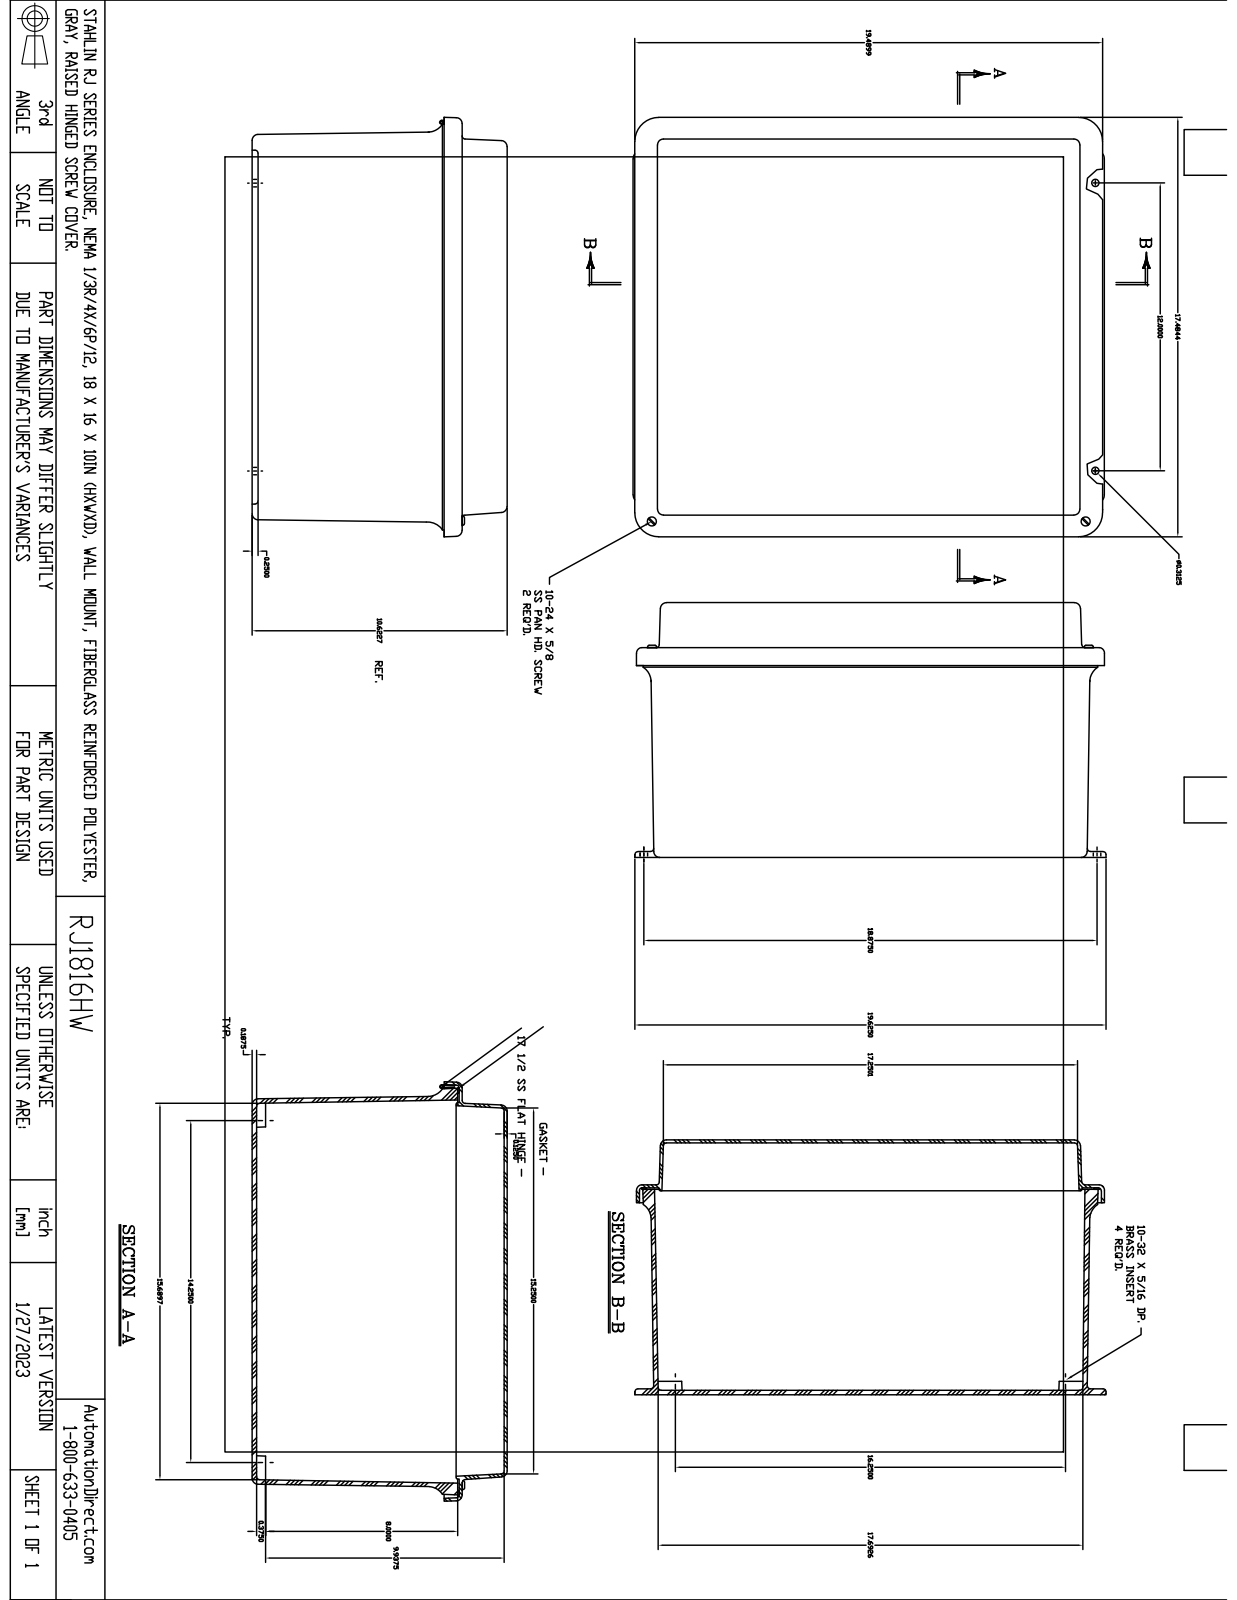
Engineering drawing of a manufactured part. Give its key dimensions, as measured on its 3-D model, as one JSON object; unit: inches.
{"part_name": "MR1816HW", "step_written_by": "SolidWorks 2018 (AUTOMOTIVE_DESIGN)", "units": "inches", "bodies": {"solids": 26, "faces": 1012, "planar": 390, "cylindrical": 389, "other": 233}, "overall_size": [19.625, 17.513, 10.642], "volume_in3": 249, "surface_area_in2": 2917, "round_holes": [[0.131, 12], [0.14, 12], [0.152, 5], [0.156, 4], [0.218, 4], [0.145, 2], [0.085, 1]], "round_bosses_or_shafts": [[0.25, 12], [0.125, 8], [0.27, 6], [0.125, 4], [0.19, 2], [0.156, 2], [0.155, 1], [0.155, 1]], "partial_cylinders_radius": [[0.031, 20], [0.125, 20], [0.25, 12], [0.062, 4], [0.2, 4], [0.35, 4], [0.355, 4], [0.375, 4]], "face_to_face_distances": [0.187, 0.188, 0.125, 10.517, 10.329, 10.642, 10.454, 2, 0.125, 8.642], "hole_center_spacings": [3.375, 3.375, 6.75, 10.25, 0.25, 9.75, 10, 1.37]}
